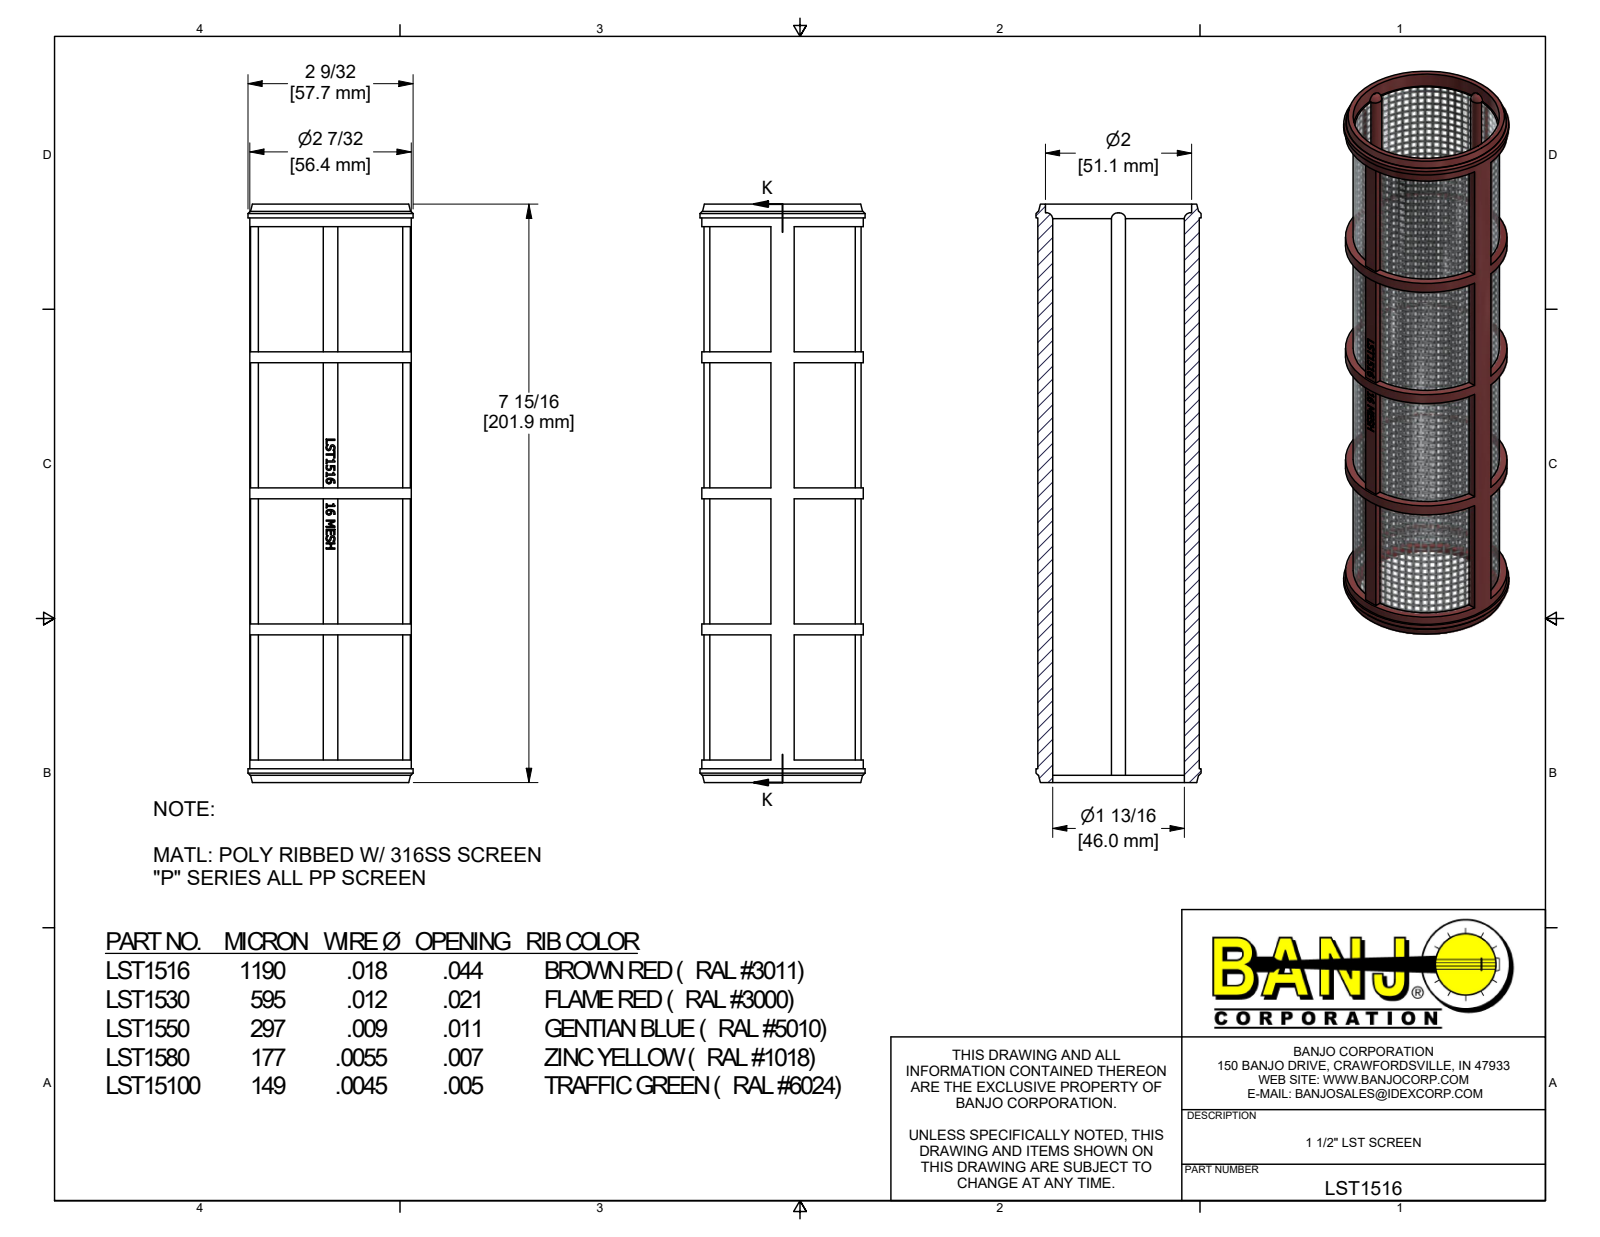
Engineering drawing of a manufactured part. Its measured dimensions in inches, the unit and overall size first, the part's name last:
Units: inches
Overall size (bounding box): 7.95 × 2.27 × 2.27
Round holes (diameter × count): ⌀1.81 ×1, ⌀1.97 ×1
Round bosses / shafts (diameter × count): ⌀2.27 ×1, ⌀2.22 ×1, ⌀2.01 ×1
Partial cylindrical surfaces — rounded edges, fillets, slot ends (radius × count): R0.1 ×4
Main face-to-face distances: 1.87, 0.92, 1.24, 3.74, 1.72, 3.59, 0.15, 0.32, 2.16, 0.2
Volume: 2.783 in³ · Surface area: 115.2 in²
Bodies: 1 solid, 465 faces (334 planar, 29 cylindrical, 102 other)
Part name (STEP PRODUCT): LST1516
STEP written by: Autodesk Inventor 2019 (AUTOMOTIVE_DESIGN)
